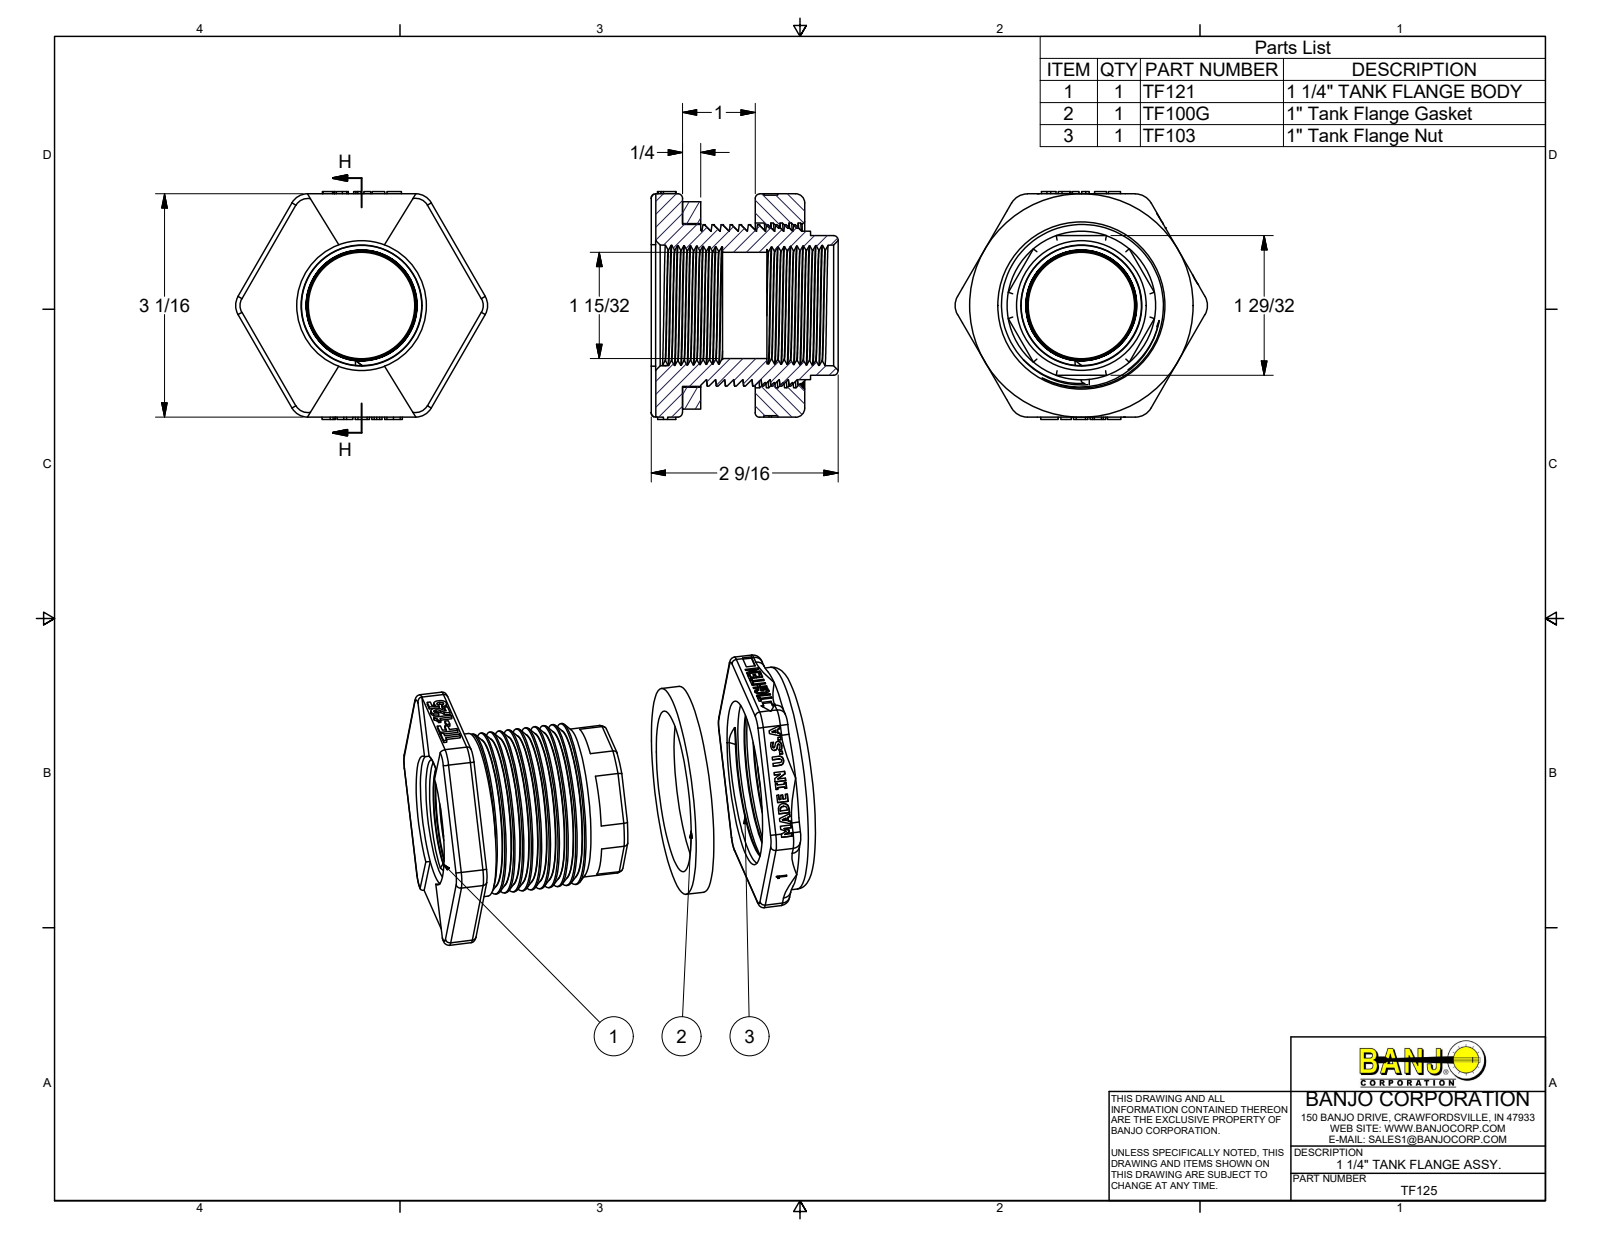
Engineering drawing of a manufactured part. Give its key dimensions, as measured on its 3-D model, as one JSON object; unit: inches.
{"part_name": "TF125; TF121; TF103; TF100G", "step_written_by": "Autodesk Inventor 2012 (AUTOMOTIVE_DESIGN)", "units": "inches", "bodies": {"solids": 3, "faces": 782, "planar": 466, "cylindrical": 73, "other": 243}, "overall_size": [3.468, 3.132, 2.57], "volume_in3": 9.315, "surface_area_in2": 89.34, "round_holes": [[1.46, 1], [1.785, 1], [2.12, 1], [2.225, 1], [2.265, 1]], "round_bosses_or_shafts": [[3.07, 1], [2.85, 1], [2.25, 1], [2.22, 1], [2.04, 1]], "partial_cylinders_radius": [[0.063, 22], [0.125, 6], [0.25, 6], [0.893, 1]], "face_to_face_distances": [0.43, 0.74, 0.31, 0.25, 0.06, 0.68, 0.74, 0.68, 0.99, 1.42]}
